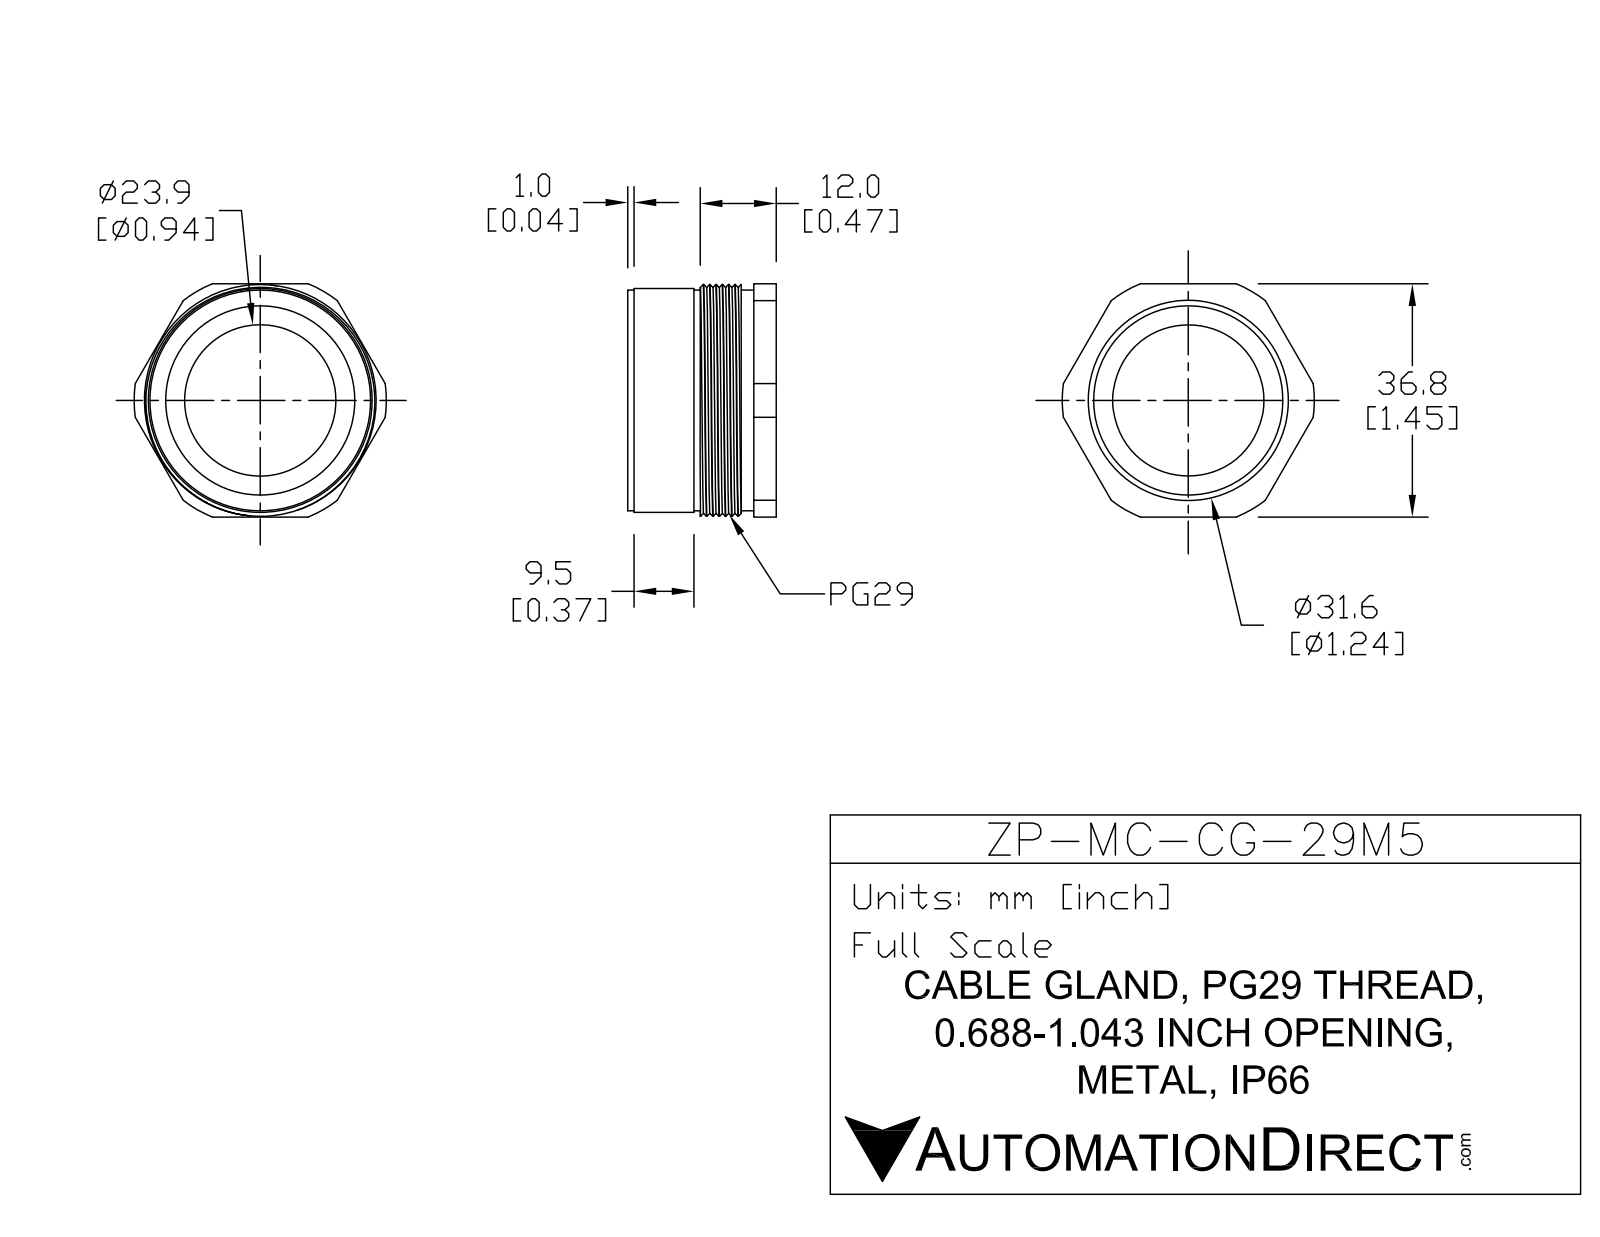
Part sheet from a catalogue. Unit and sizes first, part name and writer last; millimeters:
Units: millimetres
Overall size (bounding box): 40 × 37 × 24
Round holes (diameter × count): ⌀24 ×1, ⌀30 ×1, ⌀31.75 ×1
Round bosses / shafts (diameter × count): ⌀36.75 ×1, ⌀35.5 ×1, ⌀35 ×1
Partial cylindrical surfaces — rounded edges, fillets, slot ends (radius × count): R20 ×1
Main face-to-face distances: 9.5, 1, 10.5, 12.5, 13.5, 23, 24, 11.5, 4, 8.5
Volume: 8 802 mm³ · Surface area: 8 124 mm²
Bodies: 4 solids, 33 faces (16 planar, 15 cylindrical, 2 other)
Part name (STEP PRODUCT): ZP-MC-CG-29M5
STEP written by: SolidWorks 2011 (AUTOMOTIVE_DESIGN)
